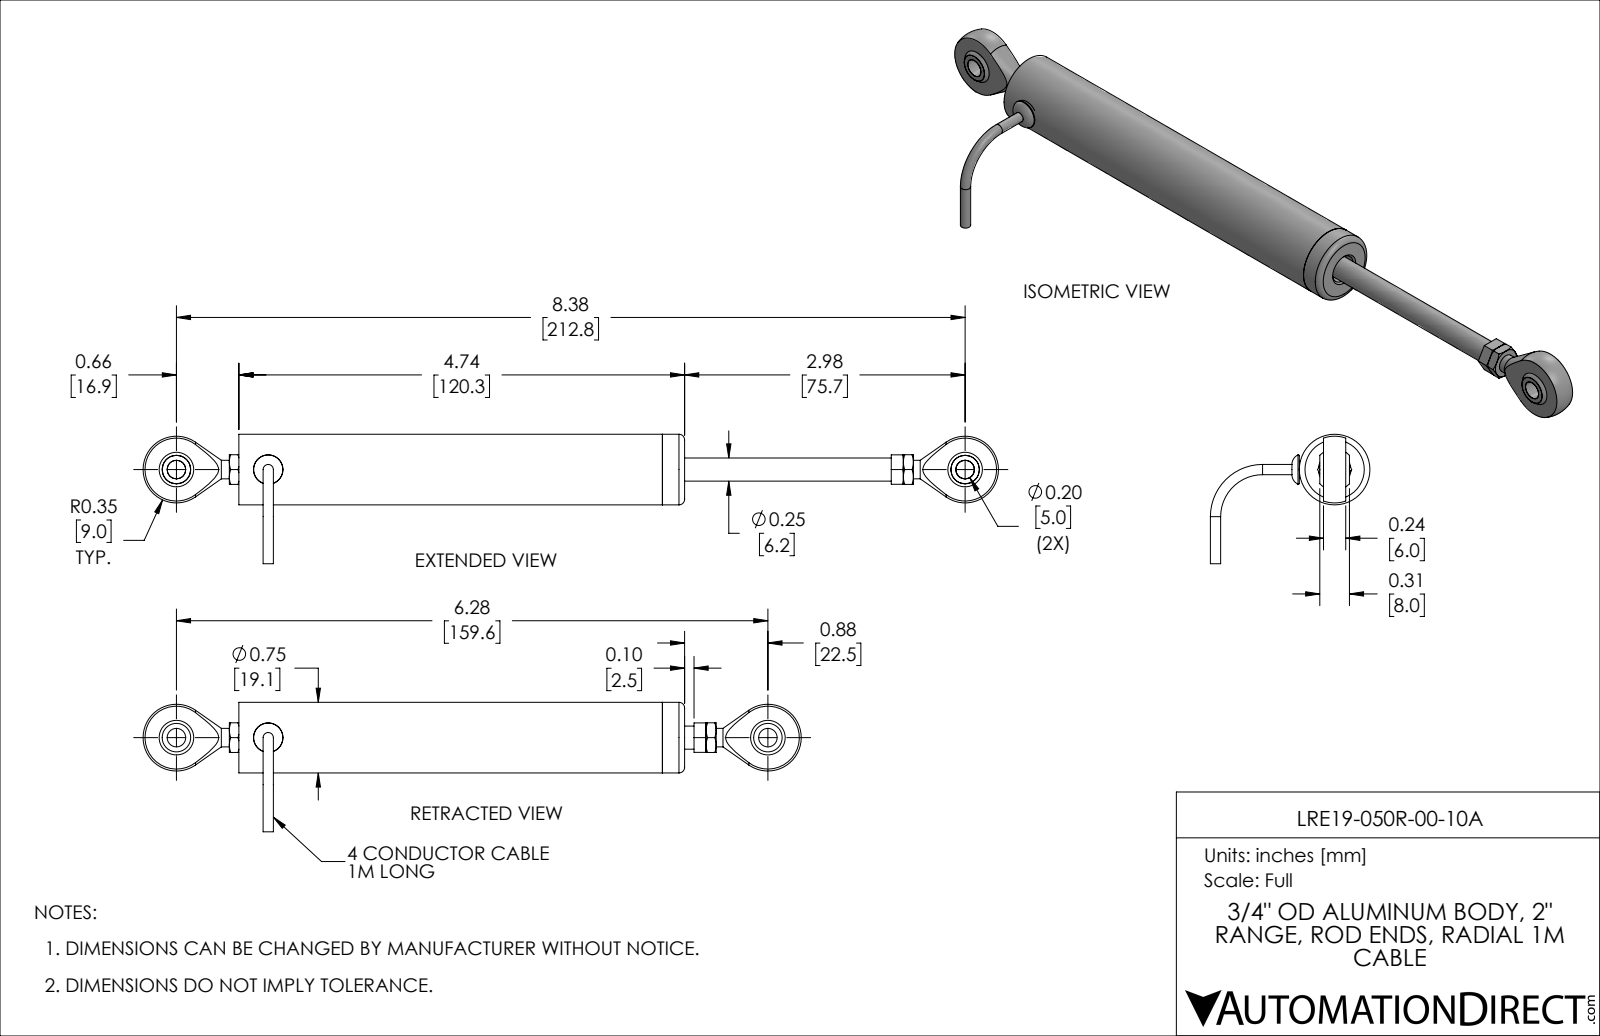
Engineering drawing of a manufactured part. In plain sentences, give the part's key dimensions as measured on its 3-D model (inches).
The part is named "LRE19-050R-00-10A". Its 3-D file was written by "SolidWorks 2019 (AUTOMOTIVE_DESIGN)". It is 13 solids with 163 faces: 58 planar, 34 cylindrical and 71 other. Overall it measures 6.952 by 1.695 by 1.375 inches. Its volume is 1.048 cubic inches and its surface area 36.81 square inches. Round holes: 3 of diameter 0.197, 1 of diameter 0.109, 1 of diameter 0.165, 1 of diameter 0.188, 1 of diameter 0.193, 1 of diameter 0.221, 1 of diameter 0.307, 1 of diameter 0.62, 1 of diameter 0.625, 1 of diameter 0.65, 1 of diameter 0.71, 1 of diameter 0.725. Round bosses or shafts: 1 of diameter 0.75, 1 of diameter 0.7, 1 of diameter 0.624, 1 of diameter 0.246, 1 of diameter 0.223, 1 of diameter 0.218, 1 of diameter 0.109. The main face-to-face distances are 0.236, 0.105, 4.626, 4.731, 4.495, 4.39, 0.236, 0.315, 0.039, 0.276. The hole center spacings are 0.975, 5.309, 6.284.
